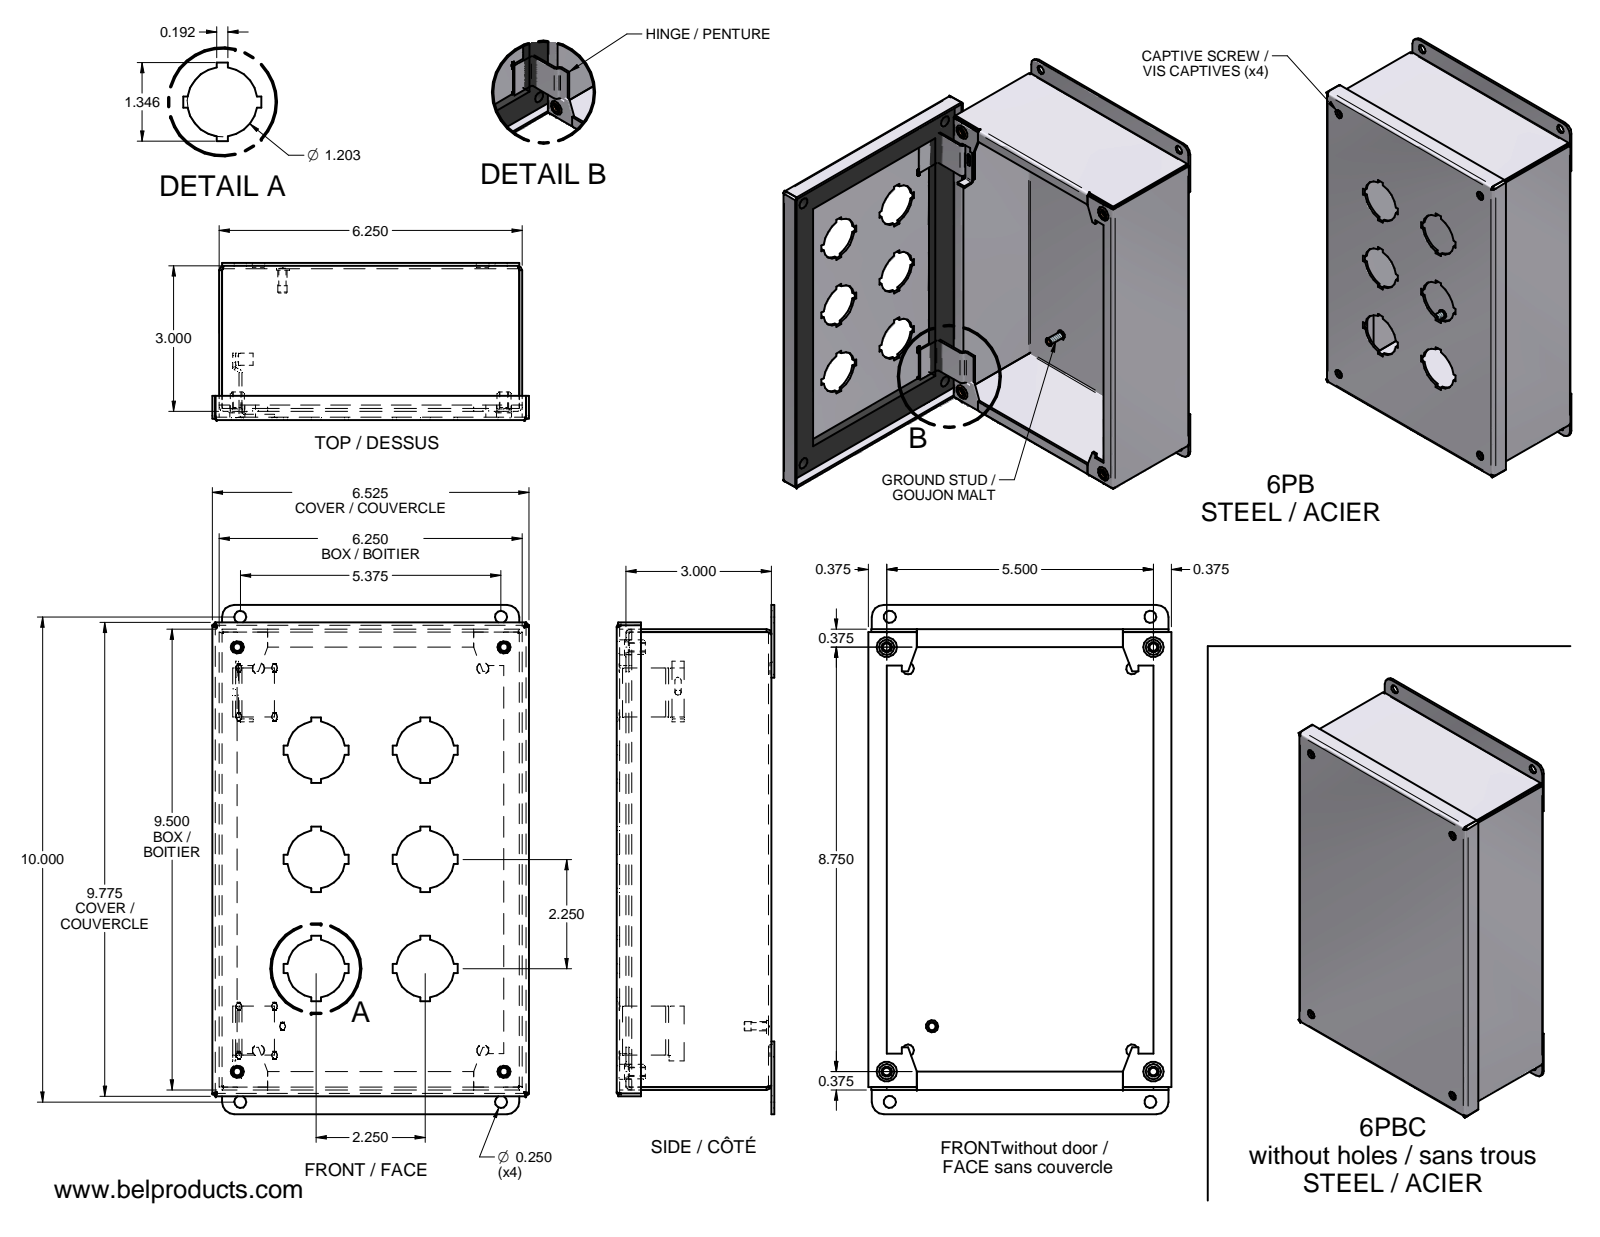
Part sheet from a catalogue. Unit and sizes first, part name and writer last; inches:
Units: inches
Overall size (bounding box): 10.5 × 6.525 × 3.245
Round holes (diameter × count): ⌀0.125 ×9, ⌀0.25 ×8, ⌀0.159 ×4, ⌀0.216 ×4, ⌀0.245 ×4, ⌀0.265 ×4, ⌀0.29 ×4, ⌀0.312 ×4, ⌀0.136 ×1
Round bosses / shafts (diameter × count): ⌀0.119 ×9, ⌀0.296 ×4, ⌀0.25 ×4, ⌀0.256 ×1, ⌀0.19 ×1, ⌀0.02 ×1
Partial cylindrical surfaces — rounded edges, fillets, slot ends (radius × count): R0.032 ×16, R0.092 ×16, R0.25 ×4, R0.063 ×2
Main face-to-face distances: 0.06, 3.125, 3.185, 0.06, 3.065, 6.19, 9.44, 0.137, 6.25, 6.13
Hole centre spacings: 5.081, 5.473, 5.5, 0.619, 0.628, 0.736, 1.01, 1.127
Volume: 20.98 in³ · Surface area: 591.3 in²
Bodies: 13 solids, 1286 faces (899 planar, 106 cylindrical, 281 other)
Part name (STEP PRODUCT): 6PBC_COUVERCLE; 6PBC-C; 6PBC_GASKET; PB-PENTURE-1 (+7 more)
STEP written by: Unknown (AUTOMOTIVE_DESIGN)
